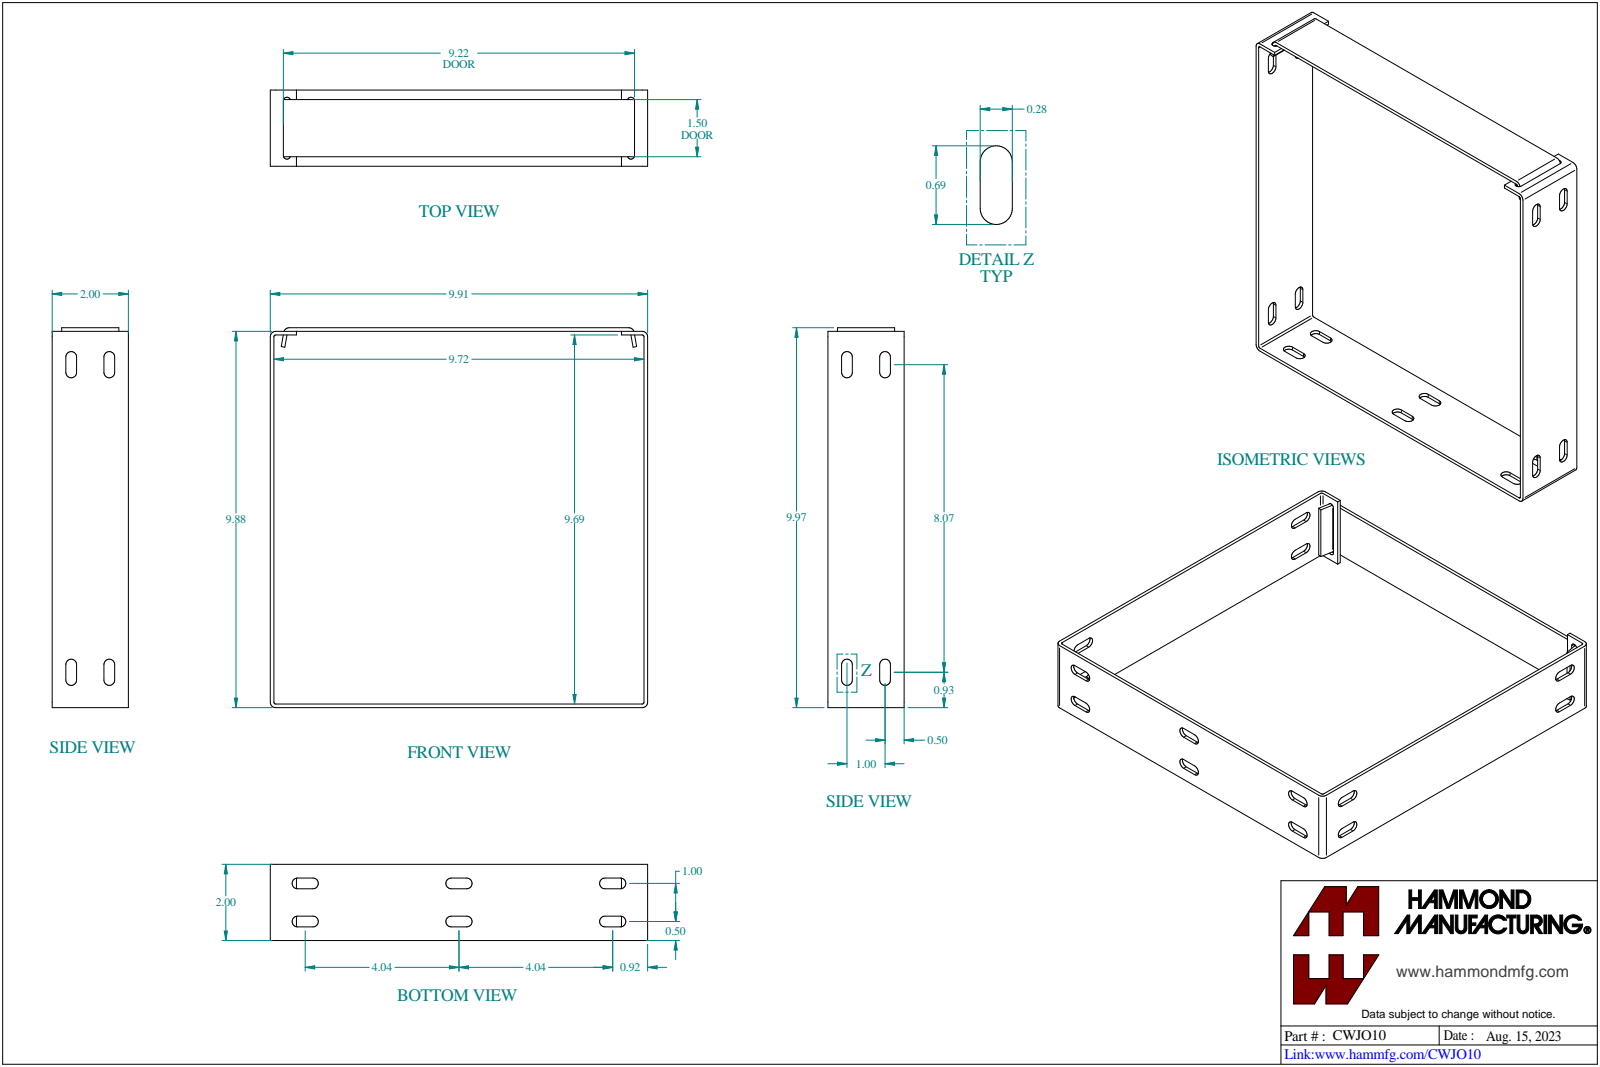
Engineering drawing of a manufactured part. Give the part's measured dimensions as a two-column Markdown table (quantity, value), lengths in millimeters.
| quantity | value |
| --- | --- |
| part name | CWJO10 |
| STEP written by | SolidWorks 2023 (CONFIG_CONTROL_DESIGN) |
| units | millimeters |
| bodies | 2 solids, 114 faces (56 planar, 58 cylindrical, 0 other) |
| overall size | 253.2 × 251.6 × 50.8 |
| volume | 113 400 mm³ |
| surface area | 101 200 mm² |
| partial cylindrical surfaces (radius × count) | 3.6 × 16, 1.2 × 6, 3.6 × 6, 2.4 × 4, 3.6 × 4 |
| main face-to-face distances | 2.4, 249.2, 2.4, 251.6, 246.8, 248.4, 250.8, 250.8, 253.2, 50.8 |
